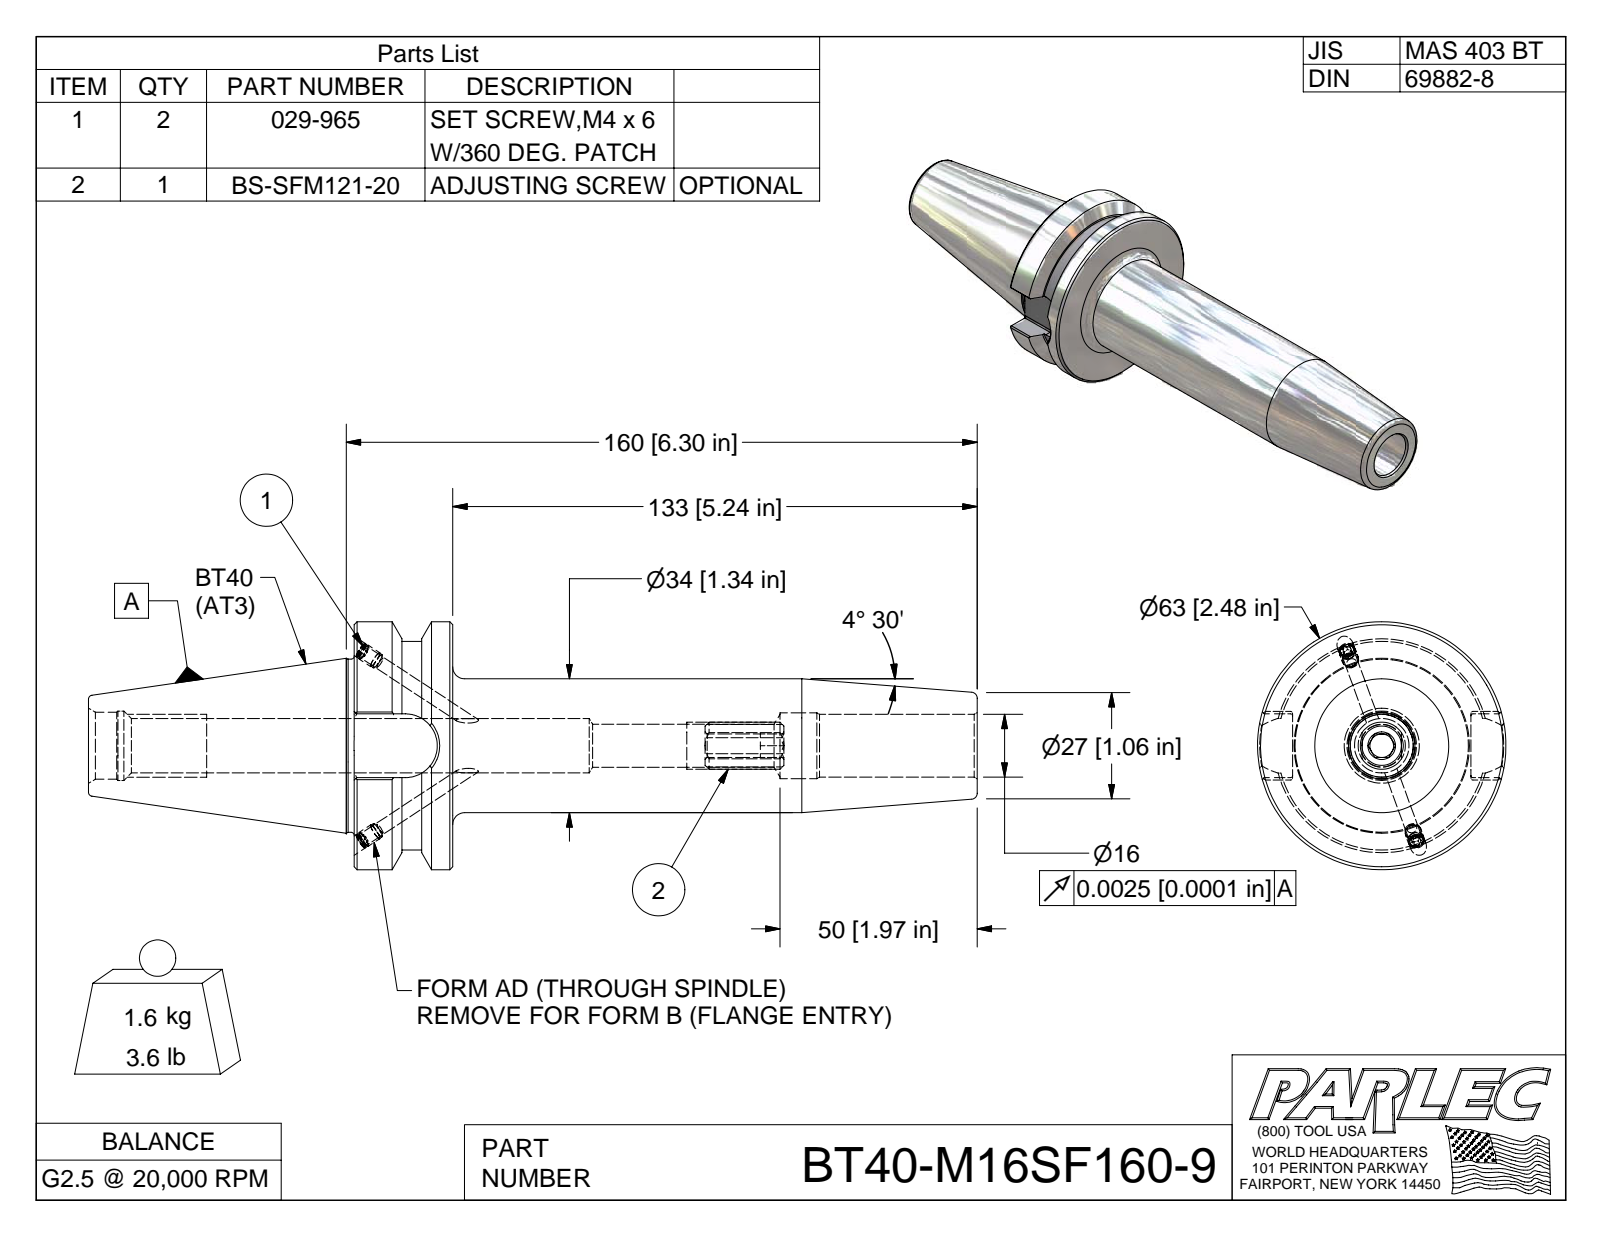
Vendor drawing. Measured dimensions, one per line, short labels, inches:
name: BT40-M16SF160-9; BT40BC-M16SF160-9-1; 029-965; BS-SFM121-20
written by: Autodesk Inventor 2009 (AUTOMOTIVE_DESIGN)
unit: in
bodies: 4 solids, 131 faces (57 planar, 33 cylindrical, 41 other)
size: 8.874 × 2.48 × 2.48
volume: 13.03 in³; area: 67.27 in²
holes: 2× ⌀0.13, 2× ⌀0.161, 1× ⌀0.629, 1× ⌀0.659, 1× ⌀0.694
bosses: 2× ⌀0.165, 2× ⌀0.157, 1× ⌀2.48, 1× ⌀2.087, 1× ⌀1.75, 1× ⌀1.73, 1× ⌀1.339
rounds: 8× R0.02, 1× R0.236, 1× R0.319
face distances: 0.984, 1.78, 0.693, 1.087, 6.221, 5.237, 2.653, 3.637, 8.874, 0.637
